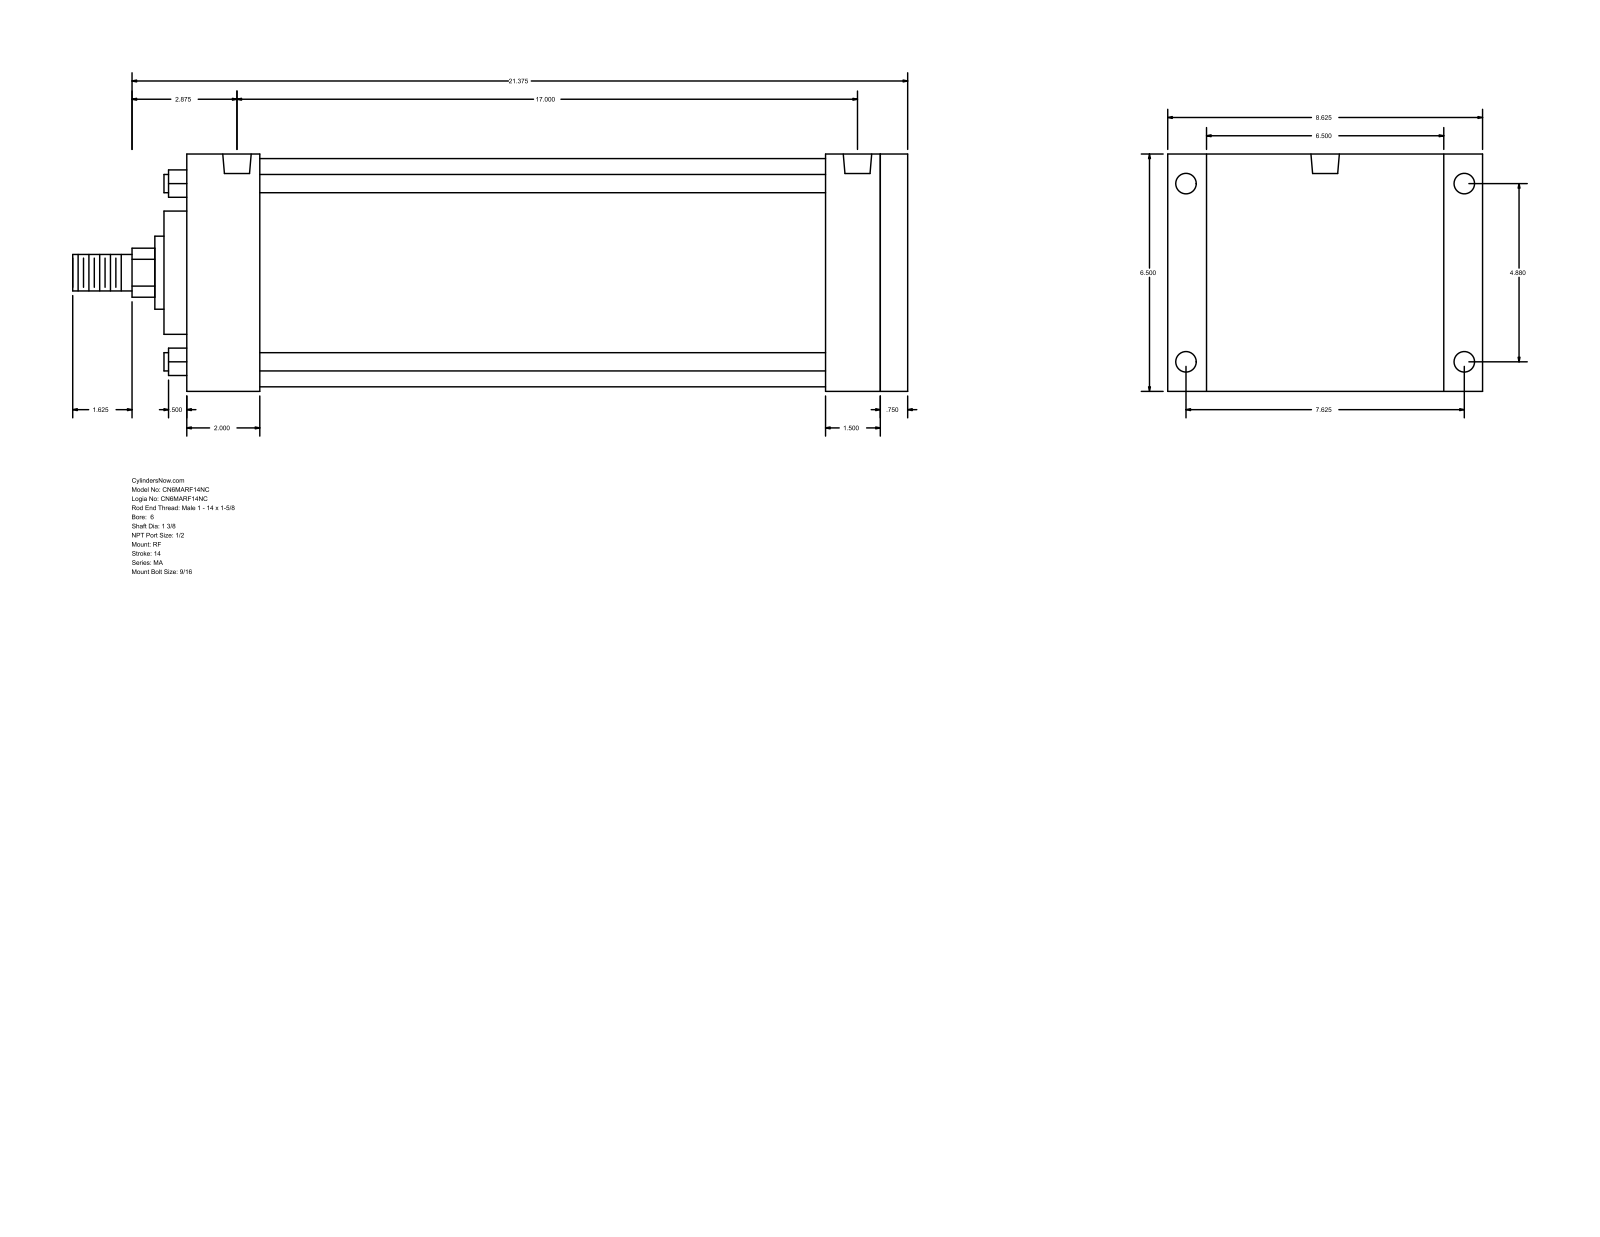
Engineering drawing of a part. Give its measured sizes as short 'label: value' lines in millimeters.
name: MA_RF__0600_1.375
written by: GSSL Pune (CONFIG_CONTROL_DESIGN)
unit: mm
bodies: 0 solids, 94 faces (65 planar, 29 cylindrical, 0 other)
size: 584.2 × 219.07 × 165.1
holes: 4× ⌀14.29, 4× ⌀17.46, 2× ⌀19.77
bosses: 4× ⌀12.7, 1× ⌀158.75, 1× ⌀85.72, 1× ⌀50.8, 1× ⌀34.92, 1× ⌀25.4
rounds: 1× R17.06
face distances: 165.1, 504.82, 485.78, 19.04, 57.15, 50.8, 434.98, 454.02, 447.67, 396.87
hole spacings: 123.96, 193.68, 229.95, 434.97, 3.18, 431.79
